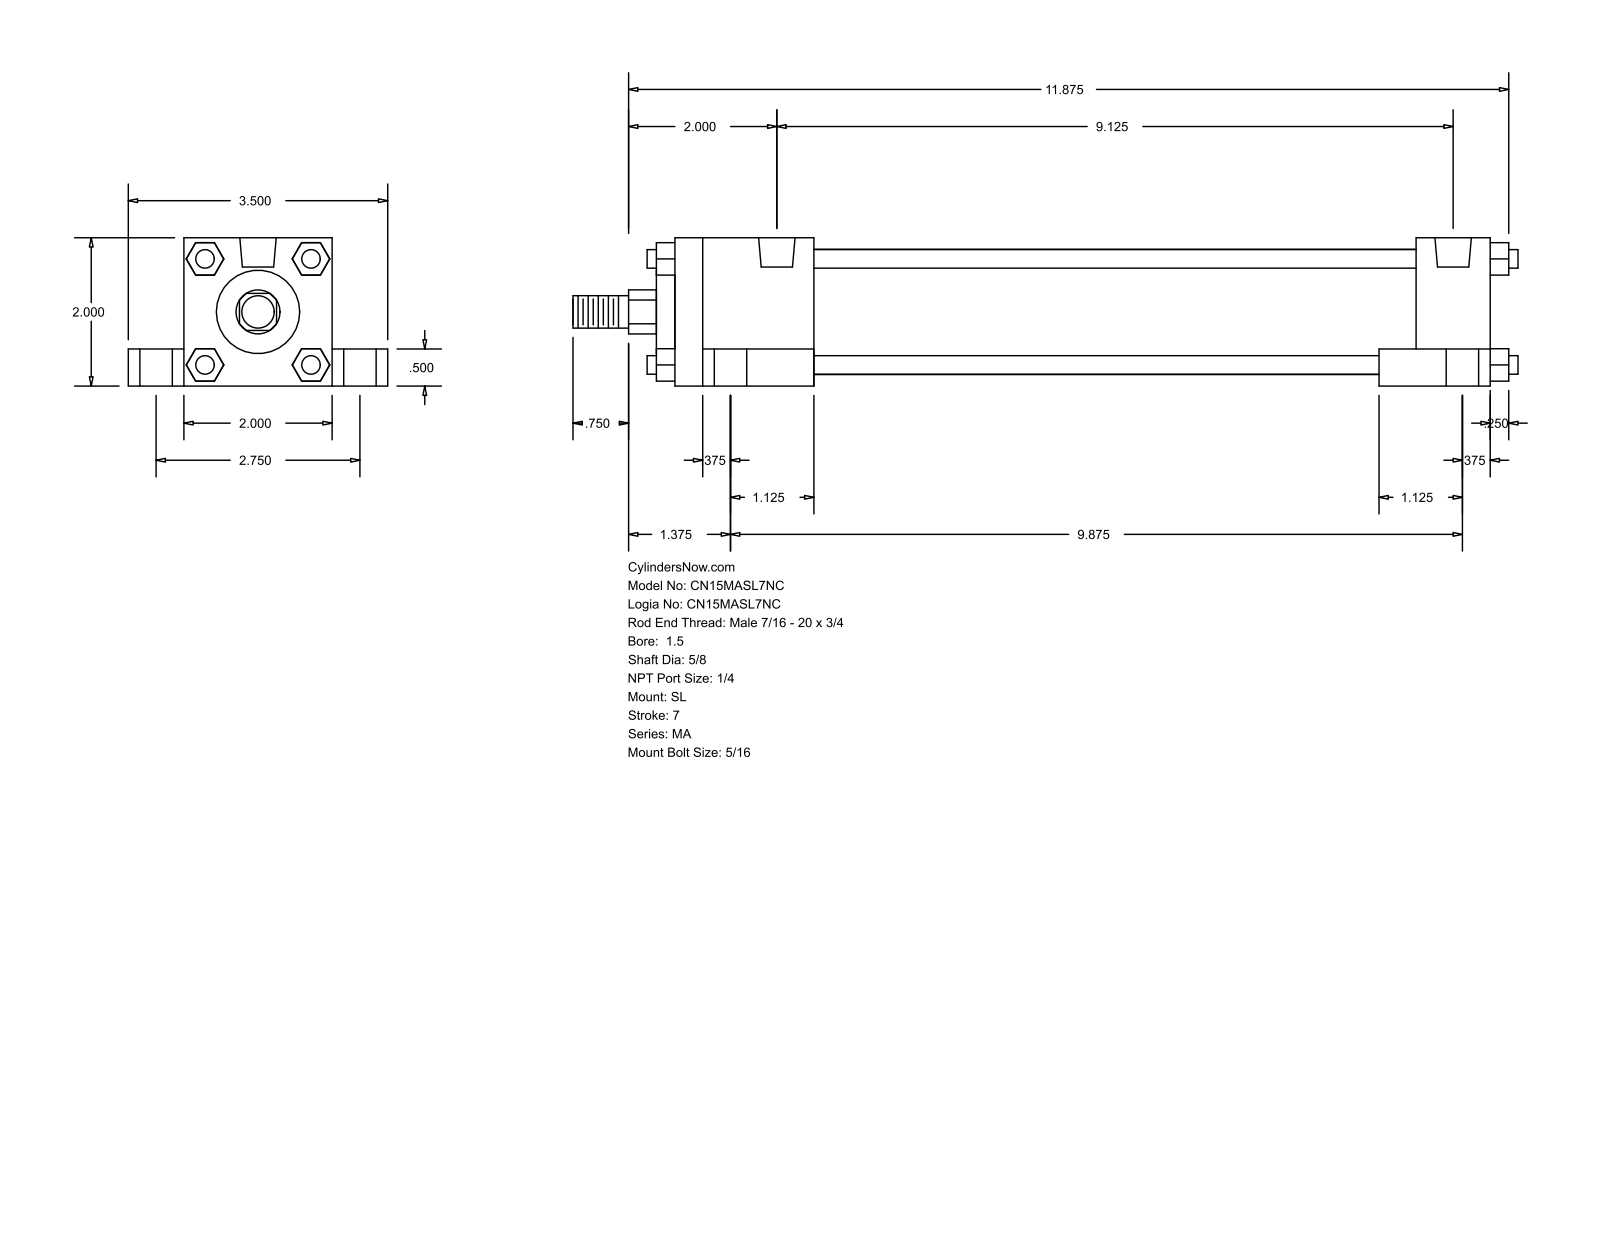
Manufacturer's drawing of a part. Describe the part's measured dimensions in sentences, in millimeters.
The part is named "MA_SL__0150_0.625". Its 3-D file was written by "GSSL Pune (CONFIG_CONTROL_DESIGN)". It is 0 solids with 148 faces: 112 planar, 36 cylindrical and 0 other. Overall it measures 323.85 by 88.9 by 50.8 millimeters. Round holes: 4 of diameter 7.94, 4 of diameter 11.11, 4 of diameter 17.46, 2 of diameter 12.49. Round bosses or shafts: 4 of diameter 6.35, 1 of diameter 42.93, 1 of diameter 28.57, 1 of diameter 15.88, 1 of diameter 11.11. Partial cylindrical surfaces (rounded edges, fillets, slot ends): 1 of radius 7.54. The main face-to-face distances are 50.8, 19.05, 38.1, 69.85, 12.7, 279.39, 6.35, 9.52, 285.74, 254. The hole center spacings are 35.06, 38.36, 69.84, 231.77, 237.53, 250.1, 250.83, 260.37.
